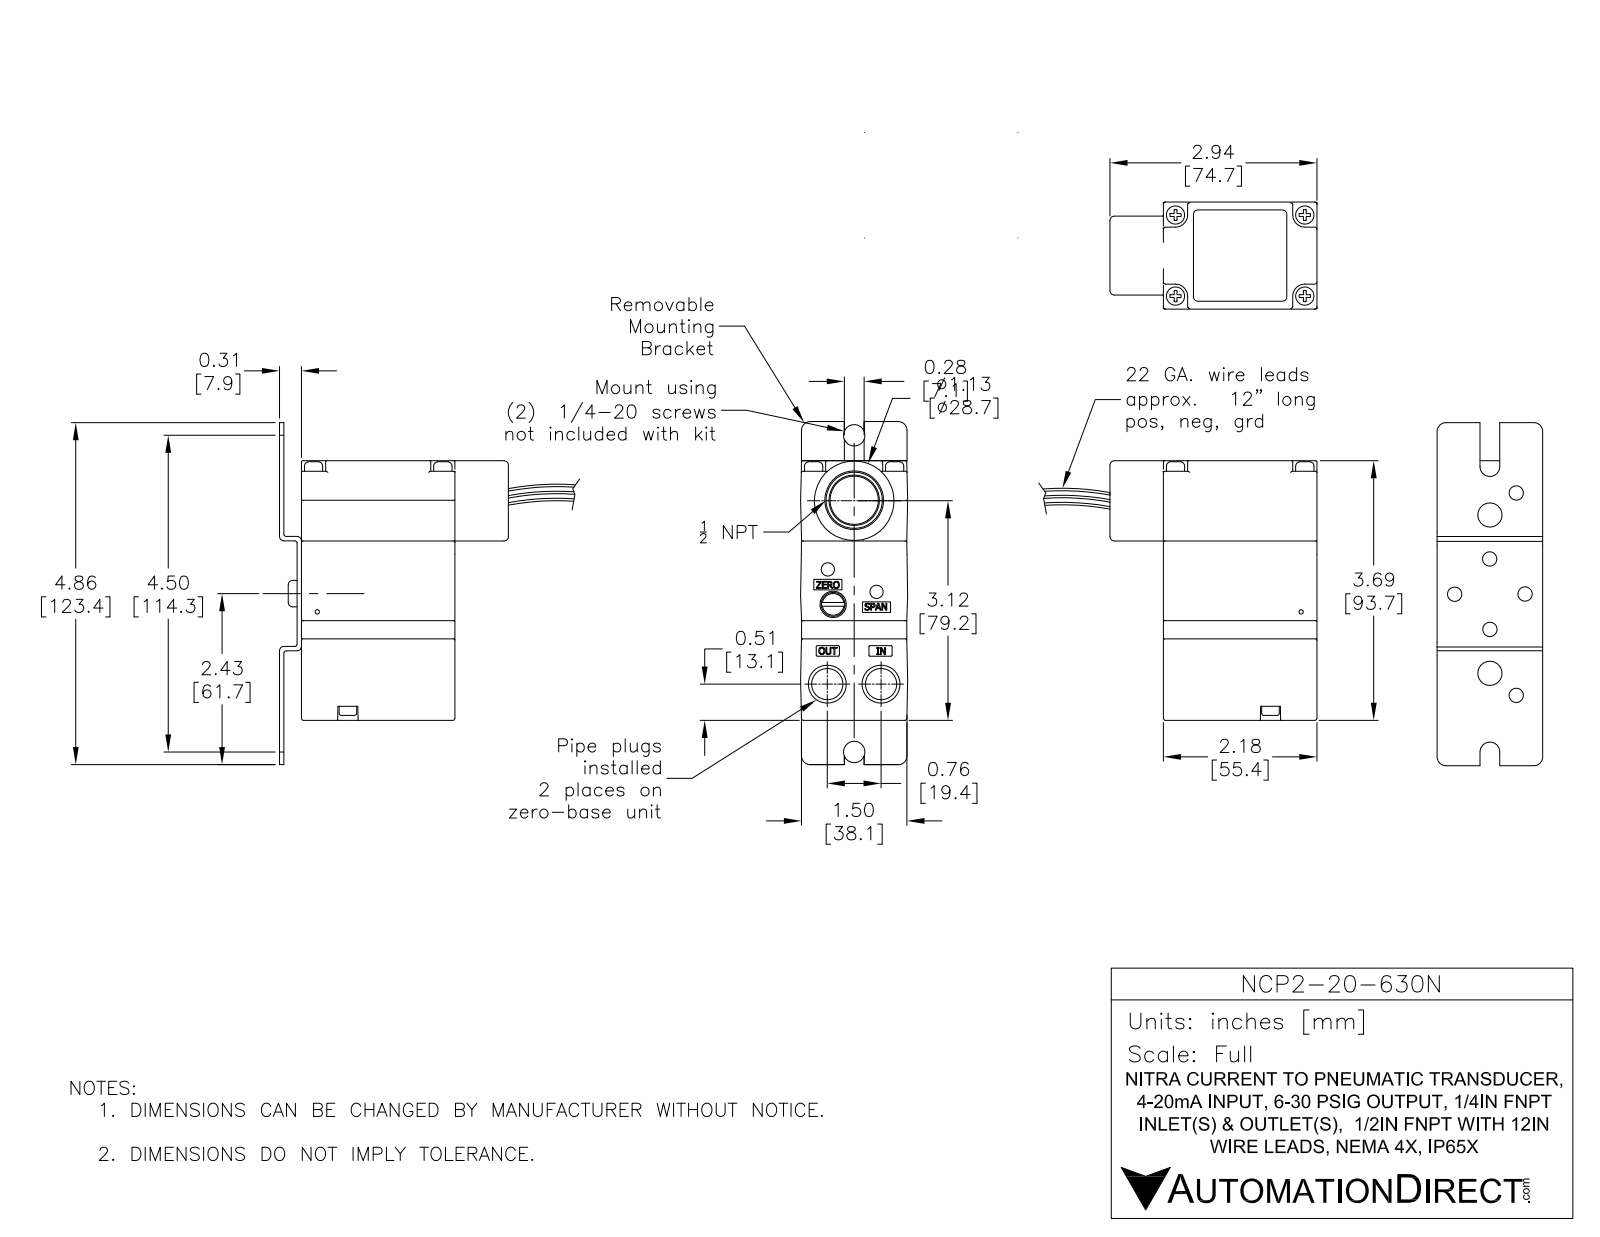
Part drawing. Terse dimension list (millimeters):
name: NCP2-20-630N
written by: SolidWorks 2016 (AUTOMOTIVE_DESIGN)
unit: mm
bodies: 4 solids, 1003 faces (537 planar, 291 cylindrical, 175 other)
size: 124.1 × 83.35 × 39.12
volume: 189 475 mm³; area: 49 479 mm²
holes: 6× ⌀5.16, 3× ⌀3.37, 2× ⌀3.18, 2× ⌀3.3, 2× ⌀4.8, 2× ⌀8.73, 2× ⌀11.38, 1× ⌀1.59, 1× ⌀3.17, 1× ⌀7.37, 1× ⌀17.48, 1× ⌀20.07
bosses: 4× ⌀6.6, 3× ⌀6.35, 2× ⌀7.49, 1× ⌀28.95, 1× ⌀16.18, 1× ⌀11.43, 1× ⌀8.66
rounds: 56× R0.76, 17× R0.5, 8× R0.4, 8× R1.59, 8× R3.17, 6× R1.47, 4× R1.25, 4× R1.27
face distances: 1.59, 6.75, 7.03, 8.62, 55.55, 37.35, 38.74, 1.39, 55.54, 62.57
hole spacings: 25.4, 12.4, 15.87, 17.74, 17.94, 17.96, 18.41, 18.78
